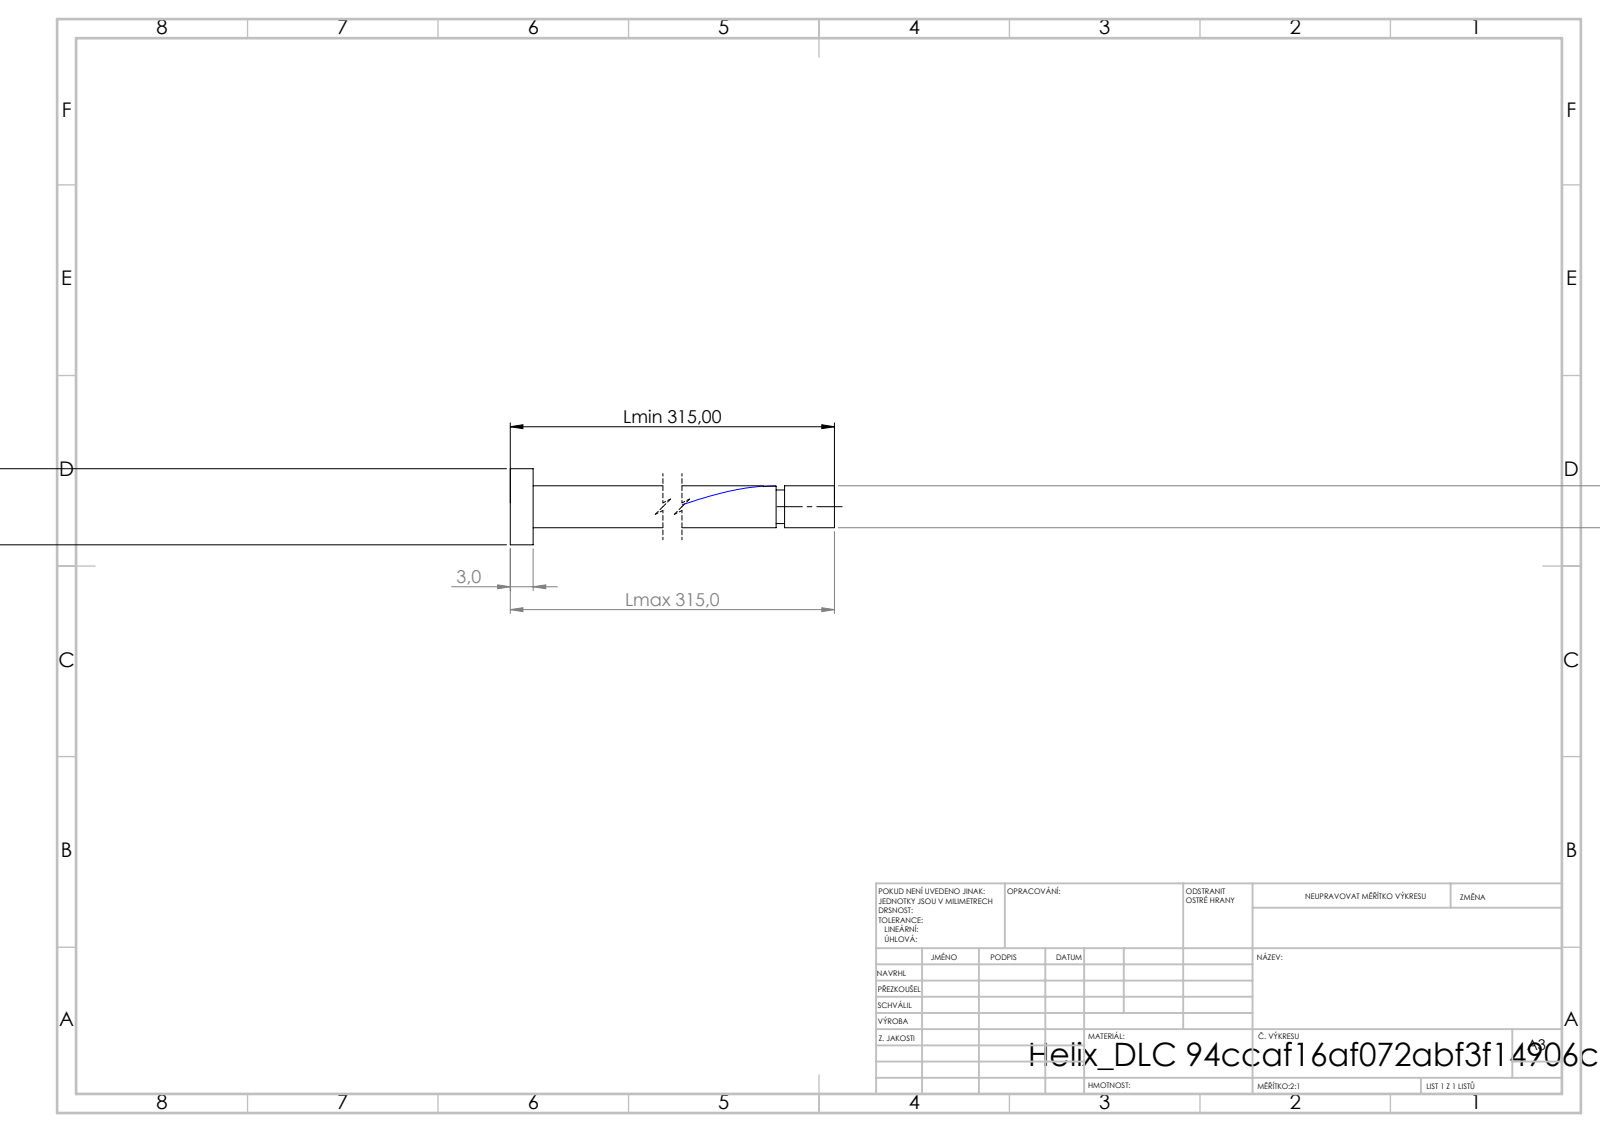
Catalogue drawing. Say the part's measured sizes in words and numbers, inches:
Its 3-D file was written by "SolidWorks 2019 (CONFIG_CONTROL_DESIGN)". It is 1 solid with 16 faces: 6 planar, 9 cylindrical and 1 other. Overall it measures 12.402 by 0.394 by 0.394 inches. Its volume is 0.563 cubic inches and its surface area 11.71 square inches. Round bosses or shafts: 1 of diameter 0.394, 1 of diameter 0.217, 1 of diameter 0.173. The main face-to-face distances are 0.118, 12.402, 12.283, 12.144, 12.026, 0.258, 12.1, 11.982, 0.043, 0.301.
